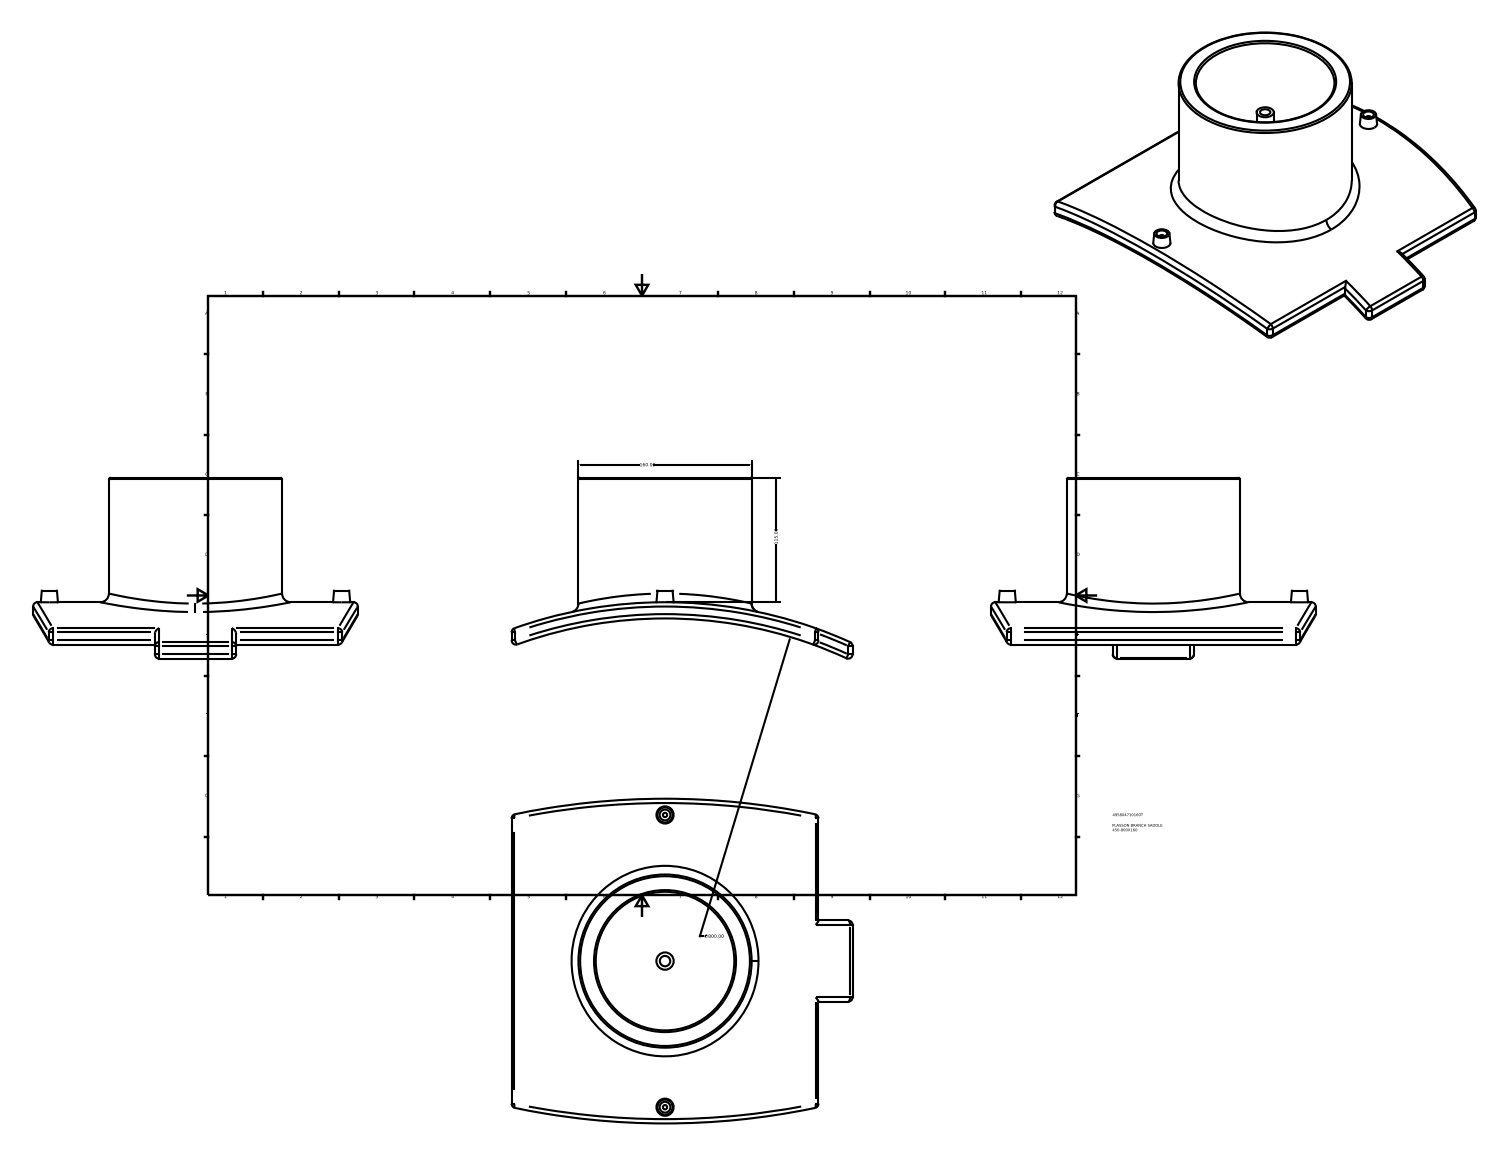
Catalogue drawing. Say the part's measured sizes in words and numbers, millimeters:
The part is named "495804710160T". Its 3-D file was written by "Autodesk Inventor 2015 (AUTOMOTIVE_DESIGN)". It is 1 solid with 66 faces: 14 planar, 27 cylindrical and 25 other. Overall it measures 315 by 300 by 167.16 millimeters. Its volume is 2 159 000 cubic millimeters and its surface area 300 392 square millimeters. Round holes: 2 of diameter 10, 1 of diameter 9.6, 1 of diameter 128. Round bosses or shafts: 2 of diameter 4, 1 of diameter 160, 1 of diameter 16. Partial cylindrical surfaces (rounded edges, fillets, slot ends): 12 of radius 4, 2 of radius 677.27, 1 of radius 400, 1 of radius 415. The main face-to-face distances are 283.5, 315, 31.5, 75, 104.4, 14, 118.4, 83.9, 69.9, 34.5. The hole center spacings are 135, 270.
